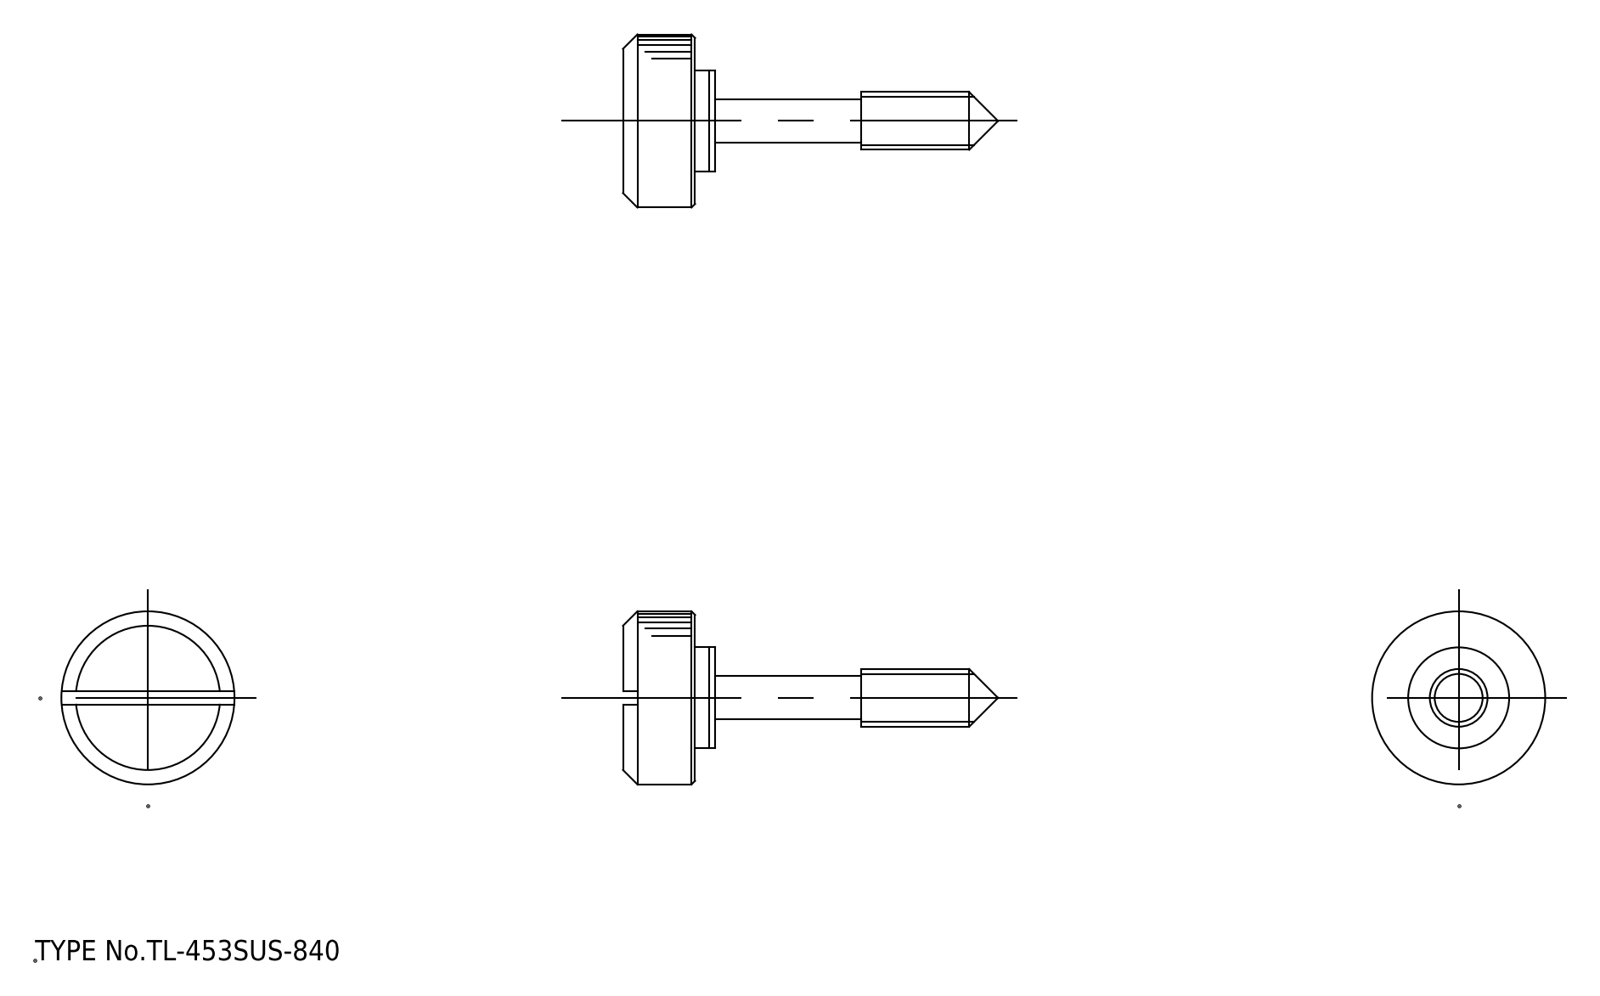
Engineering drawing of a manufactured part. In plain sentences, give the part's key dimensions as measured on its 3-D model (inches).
The part is named "washer; knob". Its 3-D file was written by "spGate 19.8.4 (****-****-****-****) (AUTOMOTIVE_DESIGN)". It is 2 solids with 42 faces: 18 planar, 18 cylindrical and 6 other. Overall it measures 2.047 by 0.945 by 0.945 inches. Its volume is 0.372 cubic inches and its surface area 4.385 square inches. Round bosses or shafts: 1 of diameter 0.945, 1 of diameter 0.551, 1 of diameter 0.315, 1 of diameter 0.236. Partial cylindrical surfaces (rounded edges, fillets, slot ends): 4 of radius 0.049, 1 of radius 0.12. The main face-to-face distances are 0.394, 0.079, 0.472, 0.504, 0.11, 0.031, 0.071, 0.315, 0.425, 1.299.
